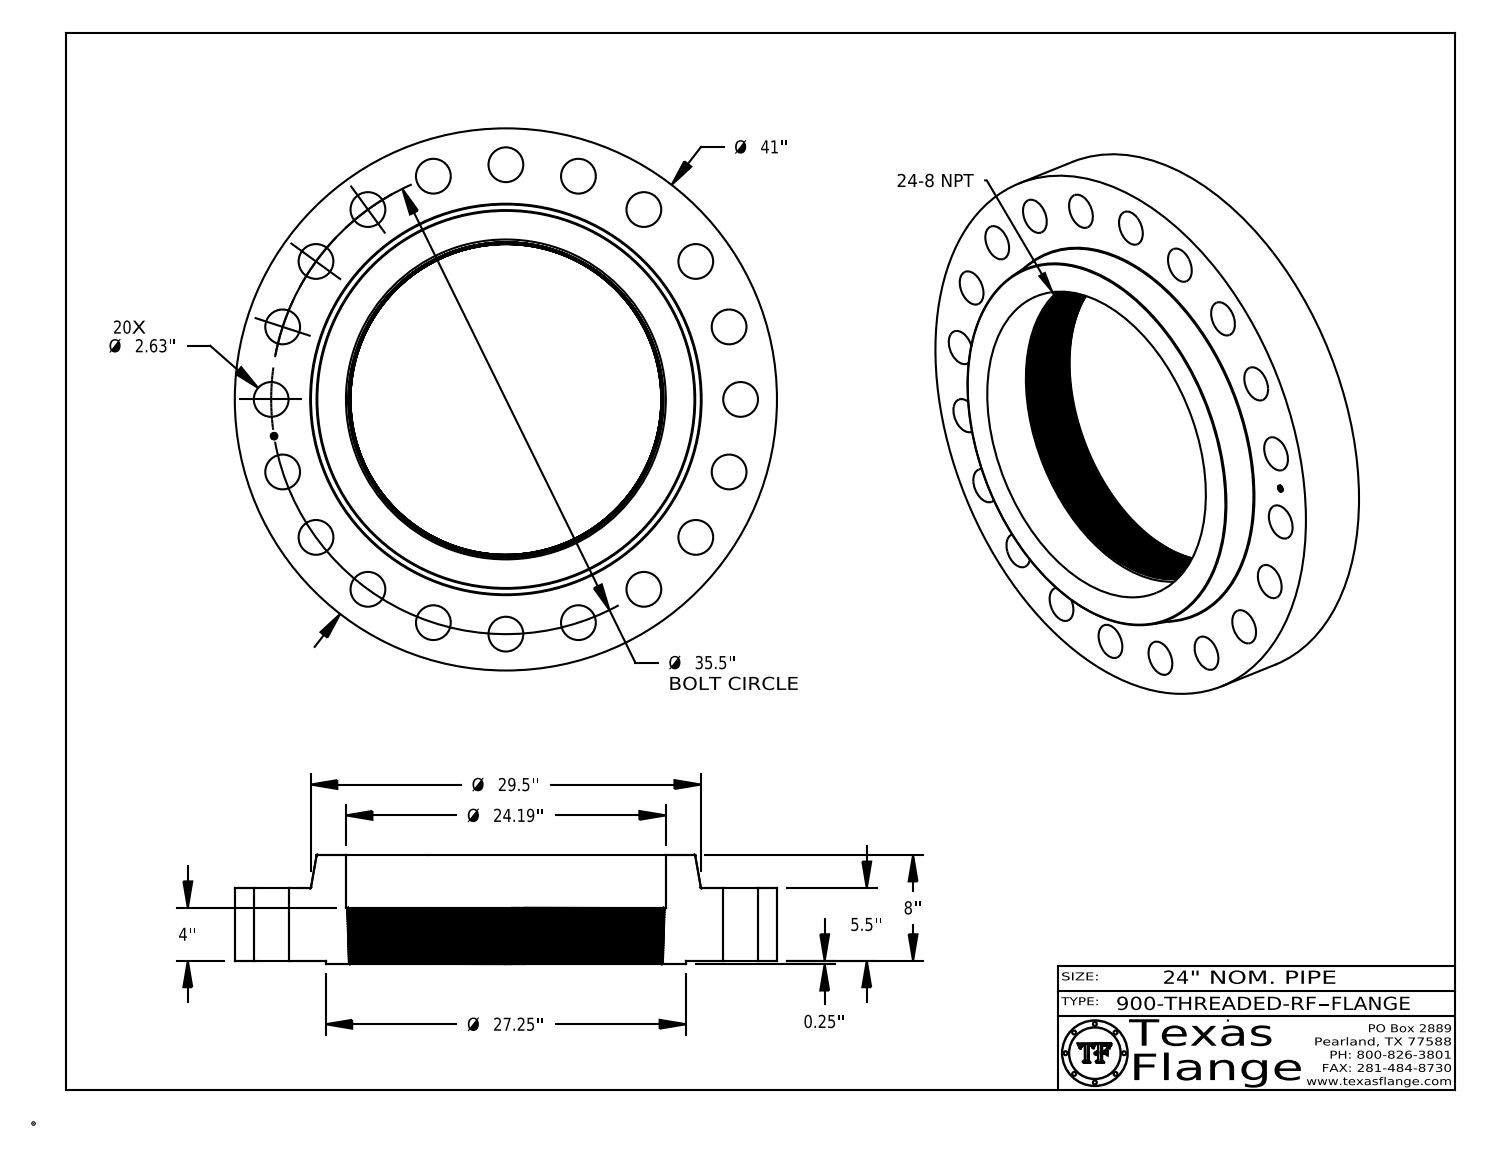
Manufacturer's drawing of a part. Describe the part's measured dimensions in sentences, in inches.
The part is named "900-THREADED-RF". Its 3-D file was written by "CATIA V5 STEP AP214 (AUTOMOTIVE_DESIGN)". It is 1 solid with 789 faces: 370 planar, 66 cylindrical and 353 other. Overall it measures 41 by 41 by 8.25 inches. Its volume is 4 750 cubic inches and its surface area 4 264 square inches. Round holes: 20 of diameter 2.63, 1 of diameter 0.495, 1 of diameter 24.19. Round bosses or shafts: 8 of diameter 0.03, 1 of diameter 41, 1 of diameter 27.25, 1 of diameter 0.39. The main face-to-face distances are 5.5, 8, 2.5, 0.25, 5.75, 8.25, 4, 4.25, 1.5, 5.735. The hole center spacings are 17.75, 10.97, 28.72, 31.631, 16.117, 20.866, 25.102, 33.762.
